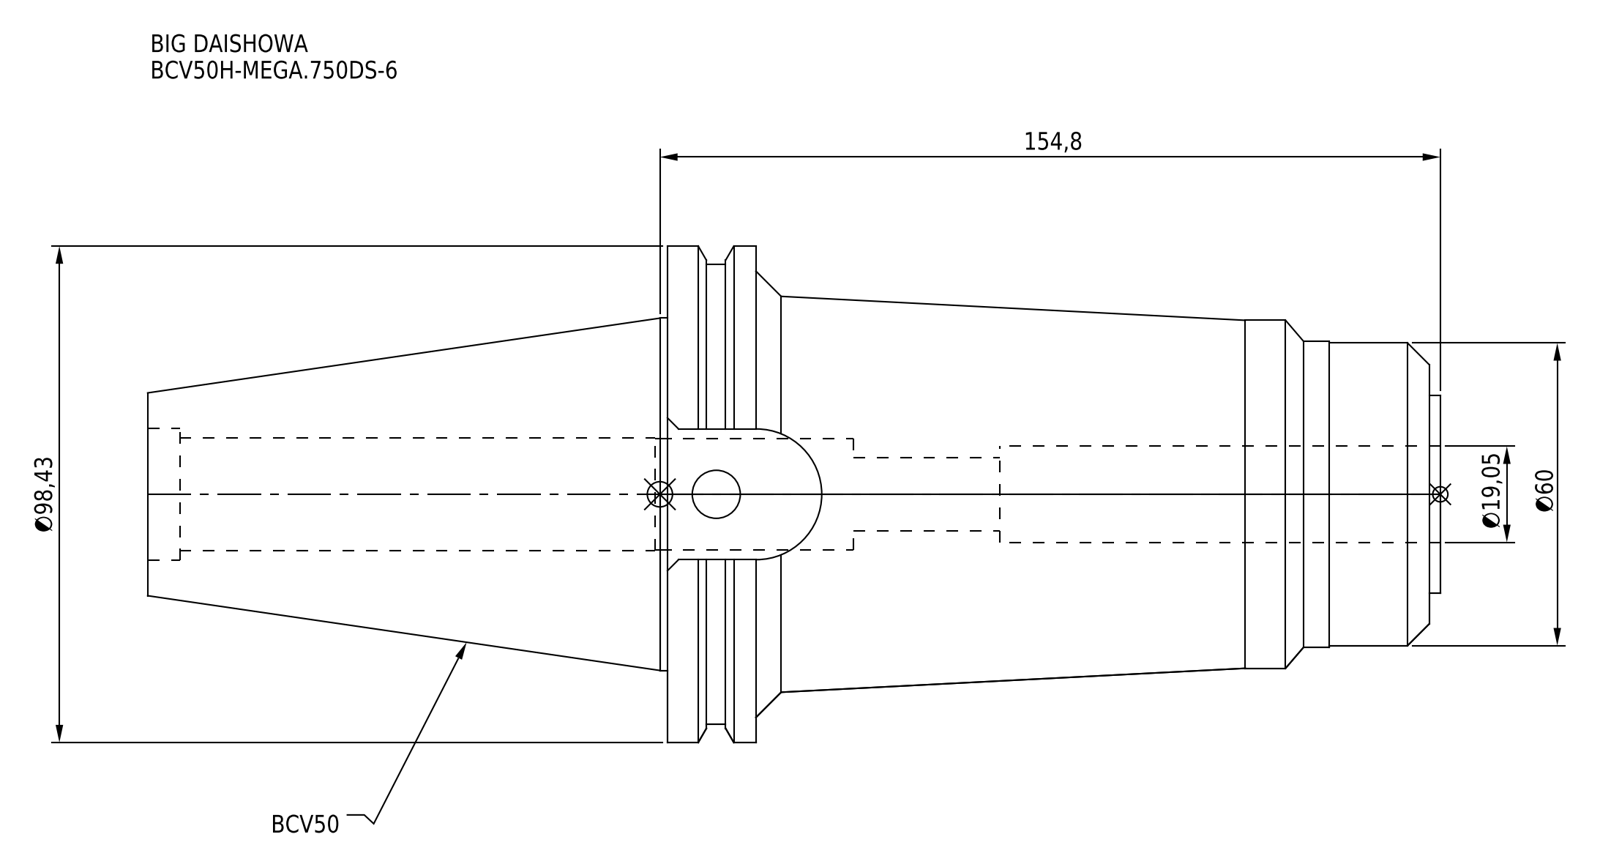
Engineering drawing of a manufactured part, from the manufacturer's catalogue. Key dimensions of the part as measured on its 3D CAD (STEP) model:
Part name (STEP PRODUCT): BCV50H-MEGA_750DS-6
STEP written by: CREO PARAMETRIC BY PTC INC, 2016380 (AUTOMOTIVE_DESIGN)
Units: millimetres
Bodies: 1 solid, 74 faces (26 planar, 34 cylindrical, 14 other)
Overall size (bounding box): 256.4 × 98.42 × 94.95
Volume: 819 053 mm³ · Surface area: 80 382 mm²
Round holes (diameter × count): ⌀9.53 ×1, ⌀14.5 ×1, ⌀19.05 ×1, ⌀22 ×1, ⌀22.3 ×1, ⌀26.23 ×1
Round bosses / shafts (diameter × count): ⌀98.42 ×1, ⌀91.29 ×1, ⌀69.85 ×1, ⌀69 ×1, ⌀60.7 ×1, ⌀60 ×1, ⌀39.3 ×1
Partial cylindrical surfaces — rounded edges, fillets, slot ends (radius × count): R12.96 ×1
Main face-to-face distances: 17.55, 135.75, 153.3, 2.2, 133.55, 151.1, 256.4, 254.2, 120.65, 103.1
